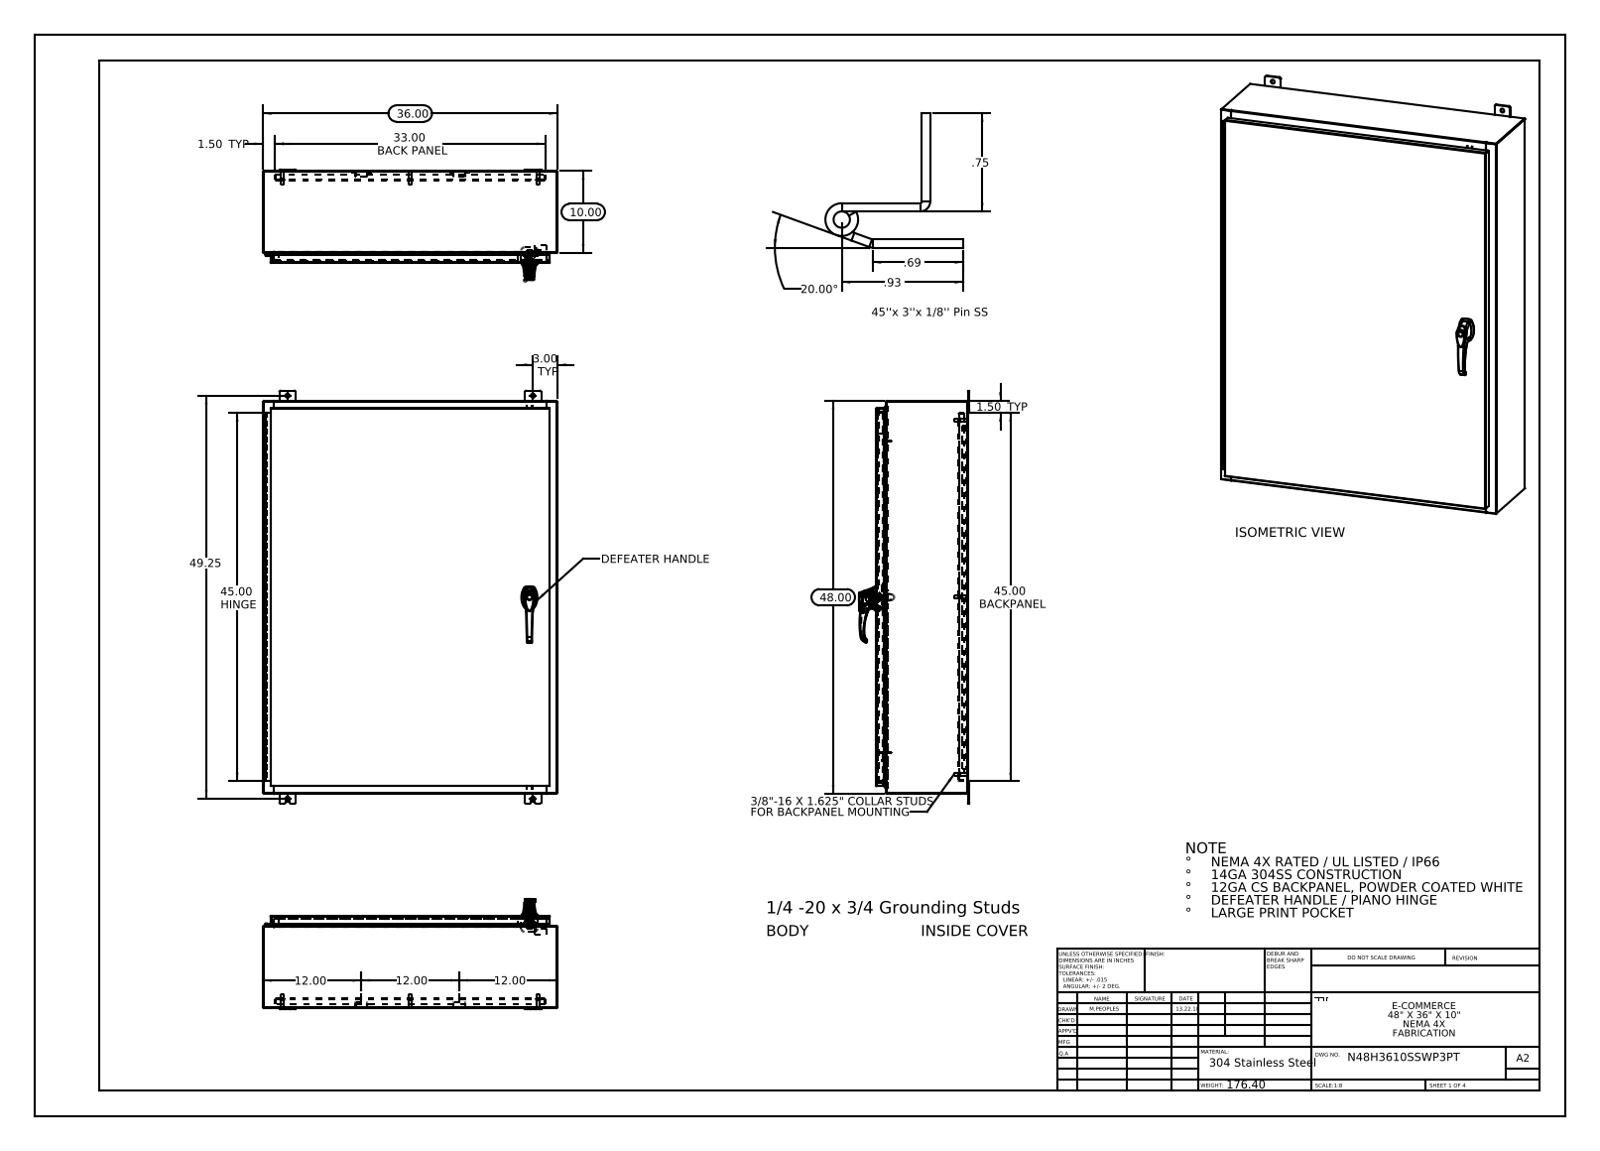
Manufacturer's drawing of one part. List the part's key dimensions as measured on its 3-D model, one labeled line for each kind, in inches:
Part name (STEP PRODUCT): N48H3610SSWP3PT Hinge Cover Side; 26161102; 00005309_G26103101; N48H3610SSWP3PT Top (+8 more)
STEP written by: SolidWorks 2013 (CONFIG_CONTROL_DESIGN)
Units: inches
Bodies: 39 solids, 3224 faces (1273 planar, 1257 cylindrical, 694 other)
Overall size (bounding box): 50.5 × 36 × 13.495
Volume: 631 in³ · Surface area: 15 635 in²
Round holes (diameter × count): ⌀0.5 ×12, ⌀0.25 ×10, ⌀0.138 ×3, ⌀0.161 ×3, ⌀0.079 ×2, ⌀0.203 ×2, ⌀0.313 ×2, ⌀0.437 ×2, ⌀0.125 ×1, ⌀0.125 ×1, ⌀0.197 ×1, ⌀0.276 ×1
Round bosses / shafts (diameter × count): ⌀0.625 ×8, ⌀0.375 ×8, ⌀0.33 ×8, ⌀1.181 ×1, ⌀0.748 ×1, ⌀0.68 ×1, ⌀0.661 ×1, ⌀0.639 ×1
Partial cylindrical surfaces — rounded edges, fillets, slot ends (radius × count): R0.118 ×37, R0.013 ×34, R0.006 ×33, R0.088 ×28, R0.19 ×24, R0.039 ×15, R0.028 ×12, R0.008 ×6
Main face-to-face distances: 0.075, 11.126, 11.051, 11.201, 0.104, 1, 10.126, 1.075, 10.051, 1.179
Hole centre spacings: 17.357, 19.665, 21.625, 38.003, 45.986, 31.25, 43.25, 0.295
